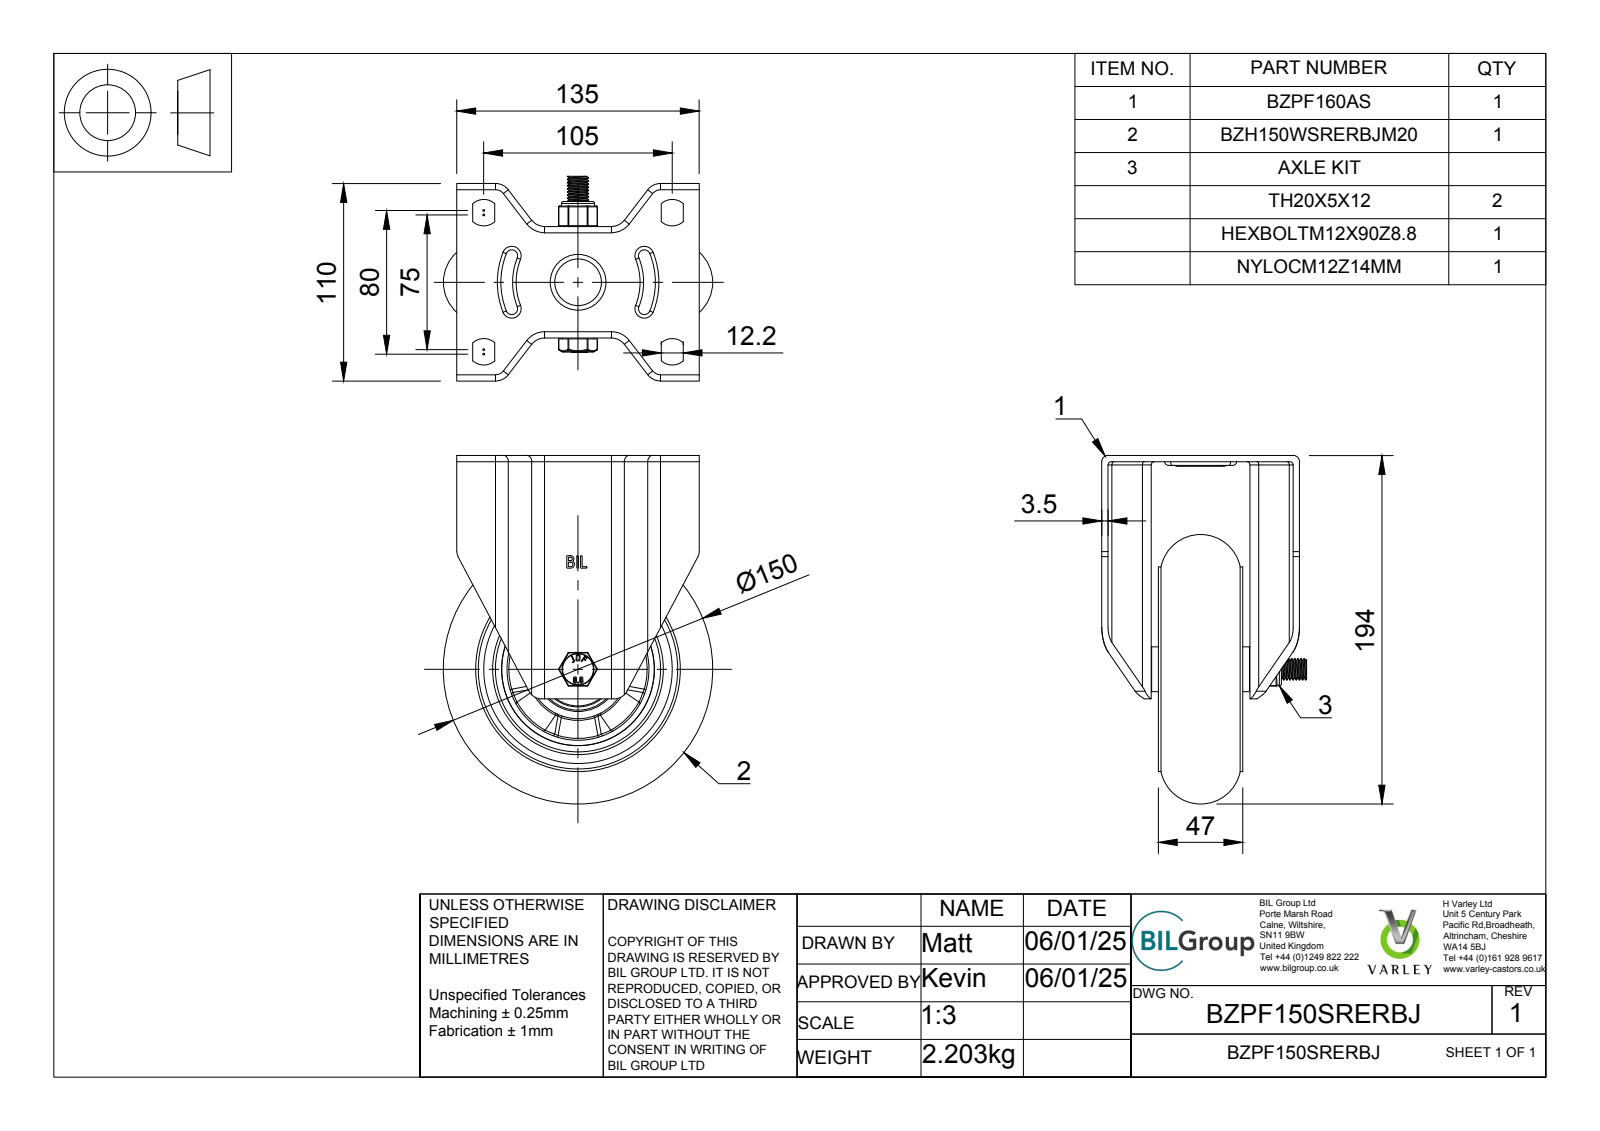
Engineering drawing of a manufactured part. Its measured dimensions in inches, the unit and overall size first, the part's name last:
Units: inches
Overall size (bounding box): 7.638 × 5.906 × 4.488
Round holes (diameter × count): ⌀0.472 ×1, ⌀0.48 ×1, ⌀0.492 ×1, ⌀0.551 ×1, ⌀0.787 ×1, ⌀1.122 ×1, ⌀1.213 ×1, ⌀1.587 ×1, ⌀1.594 ×1, ⌀1.654 ×1, ⌀1.693 ×1, ⌀1.85 ×1
Round bosses / shafts (diameter × count): ⌀4.488 ×1, ⌀3.74 ×1, ⌀2.165 ×1, ⌀1.606 ×1, ⌀1.232 ×1, ⌀1.063 ×1, ⌀0.984 ×1, ⌀0.906 ×1
Partial cylindrical surfaces — rounded edges, fillets, slot ends (radius × count): R0.02 ×20, R0.069 ×8, R0.138 ×8, R0.354 ×8, R0.358 ×8, R0.019 ×4, R0.035 ×4, R0.217 ×4
Main face-to-face distances: 0.138, 0.945, 3.248, 2.303, 0.092, 0.807, 1.083, 3.386, 4.193, 3.11
Volume: 44.11 in³ · Surface area: 366.2 in²
Bodies: 35 solids, 1279 faces (455 planar, 238 cylindrical, 586 other)
Part name (STEP PRODUCT): BZPF150SRERBJ v4; BZH150WSRERBJM20 v1; 55 SHORE A ELASTIC RUBBER TYRE; ALUMINIUM RIM (+7 more)
STEP written by: Autodesk Translation Framework v13.20.0.188 (AP242_MANAGED_MODEL_BASED_3D_ENGINEERING_MIM_LF)
